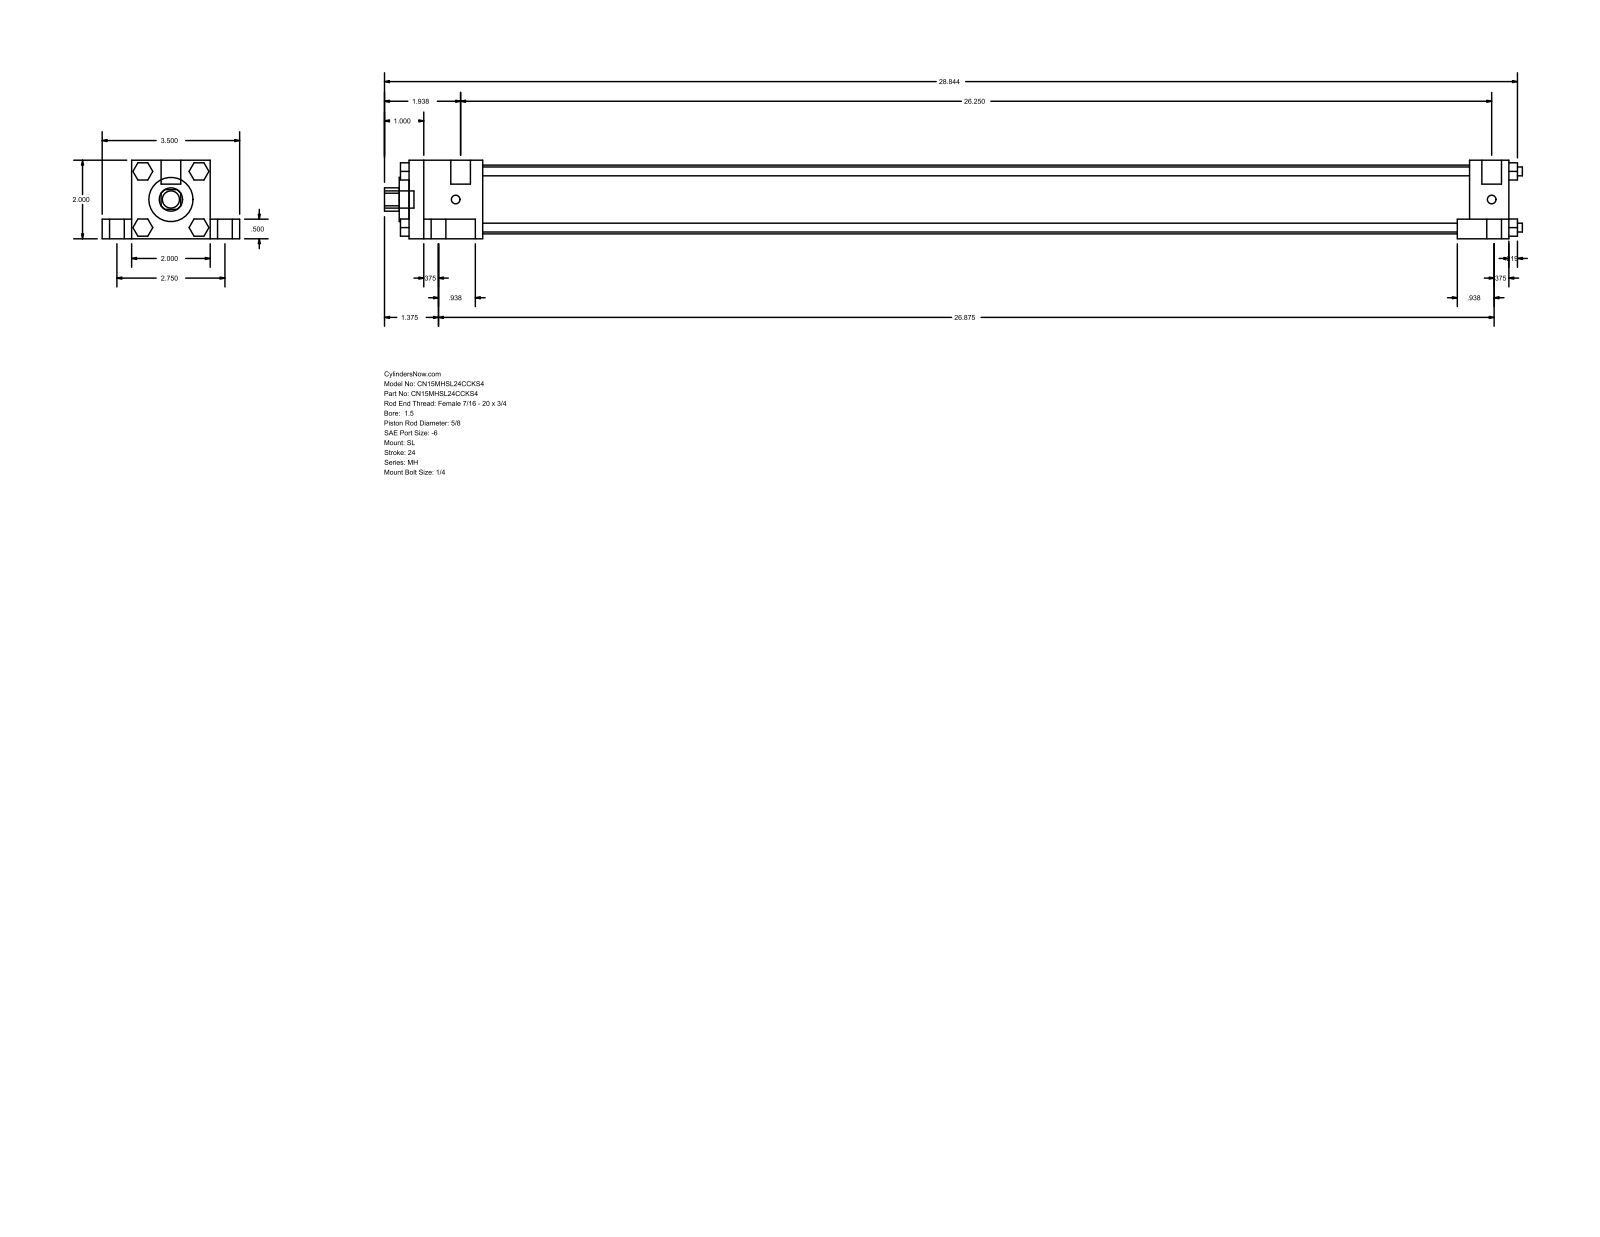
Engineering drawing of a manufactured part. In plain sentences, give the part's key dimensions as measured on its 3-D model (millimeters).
The part is named "MH_SL__0150_0.625". Its 3-D file was written by "GSSL Pune (CONFIG_CONTROL_DESIGN)". It is 0 solids with 148 faces: 112 planar, 36 cylindrical and 0 other. Overall it measures 735.81 by 88.9 by 50.8 millimeters. Round holes: 1 of diameter 15.88, 1 of diameter 28.57, 1 of diameter 44.45. Round bosses or shafts: 4 of diameter 15.88, 4 of diameter 9.53, 4 of diameter 5.71, 4 of diameter 5.56, 2 of diameter 12.7, 1 of diameter 11.11. Partial cylindrical surfaces (rounded edges, fillets, slot ends): 1 of radius 7.54. The main face-to-face distances are 50.8, 38.1, 19.05, 12.7, 69.85, 711.2, 9.52, 33.34, 668.34, 685.79.
